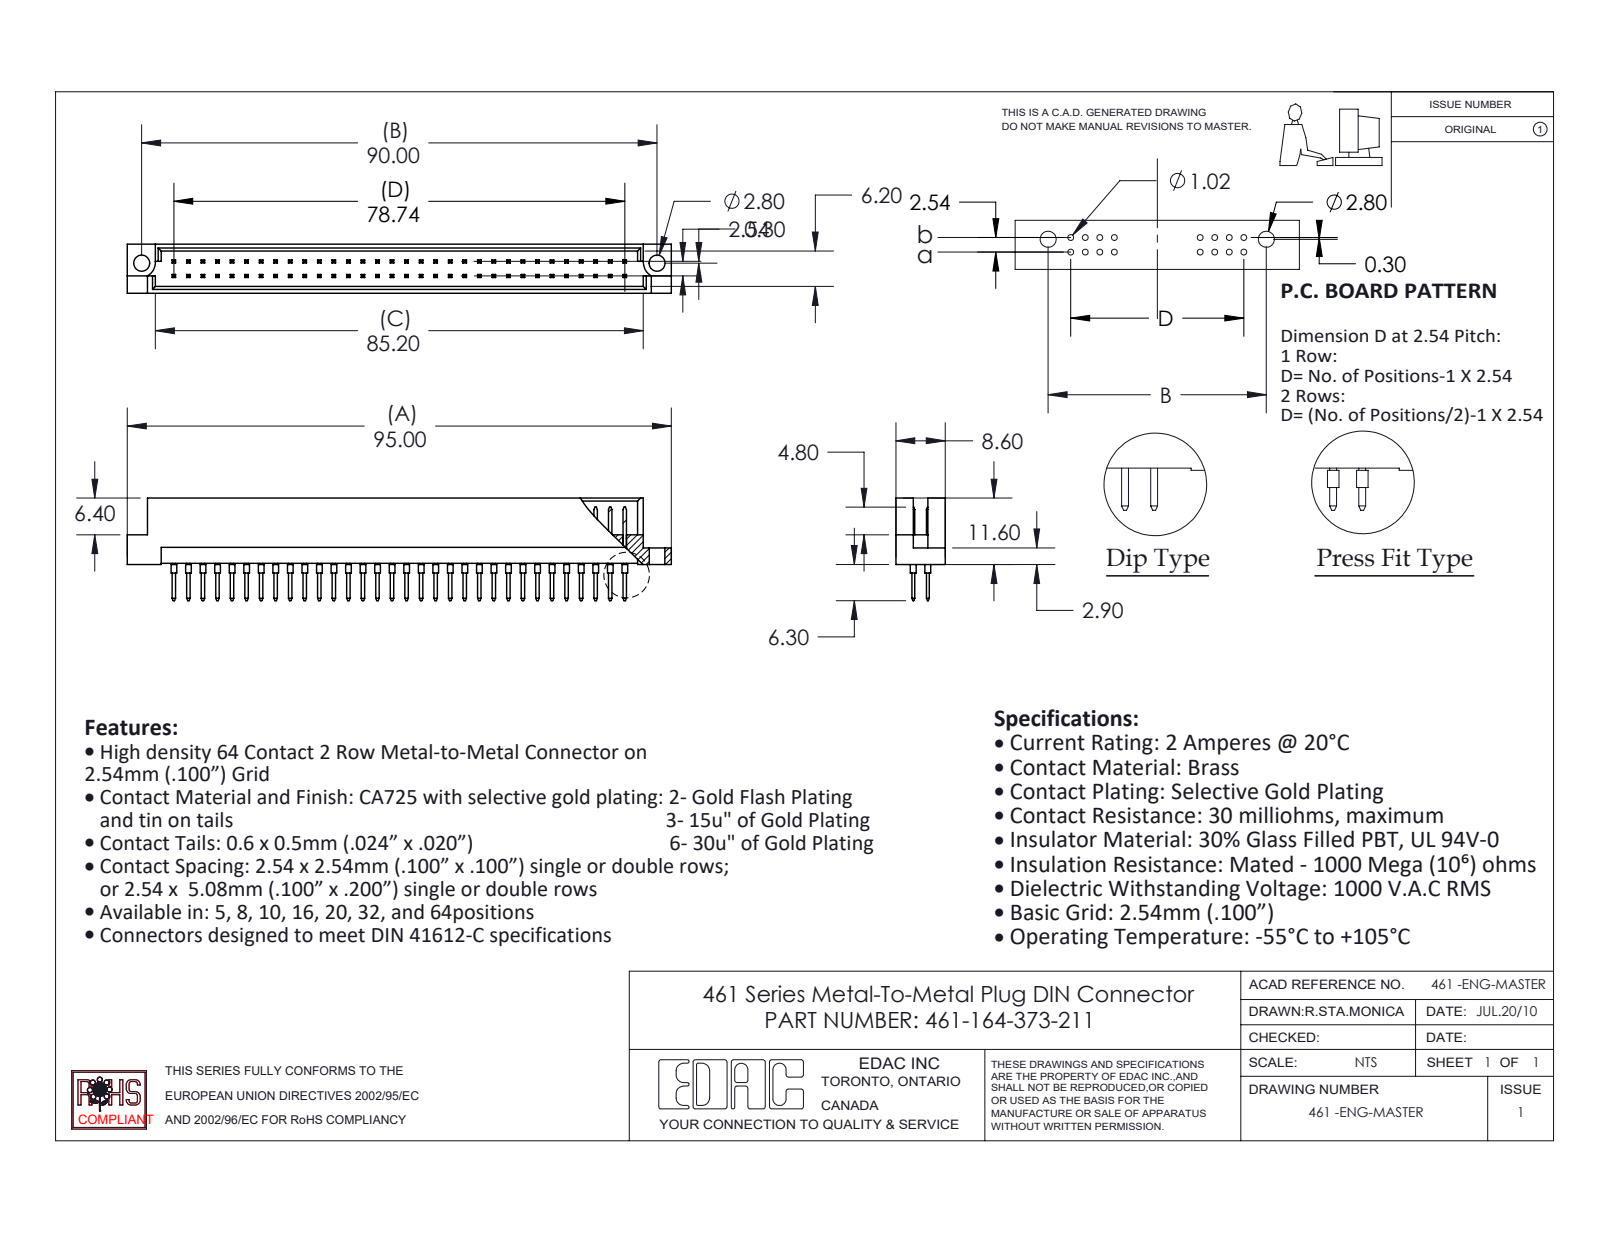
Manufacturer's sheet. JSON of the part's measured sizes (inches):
{"part_name": "461 Part_64; 461-290_73; 461-164-373-211", "step_written_by": "SolidWorks 2020 (CONFIG_CONTROL_DESIGN)", "units": "inches", "bodies": {"solids": 65, "faces": 1713, "planar": 1578, "cylindrical": 135, "other": 0}, "overall_size": [3.74, 0.705, 0.339], "volume_in3": 0.306, "surface_area_in2": 12.55, "round_holes": [[0.11, 2]], "round_bosses_or_shafts": [[0.039, 64]], "partial_cylinders_radius": [[0.11, 2]], "face_to_face_distances": [0.047, 0.291, 0.1, 0.339, 0.129, 0.209, 0.082, 0.162, 0.109, 0.229], "hole_center_spacings": [3.543]}
